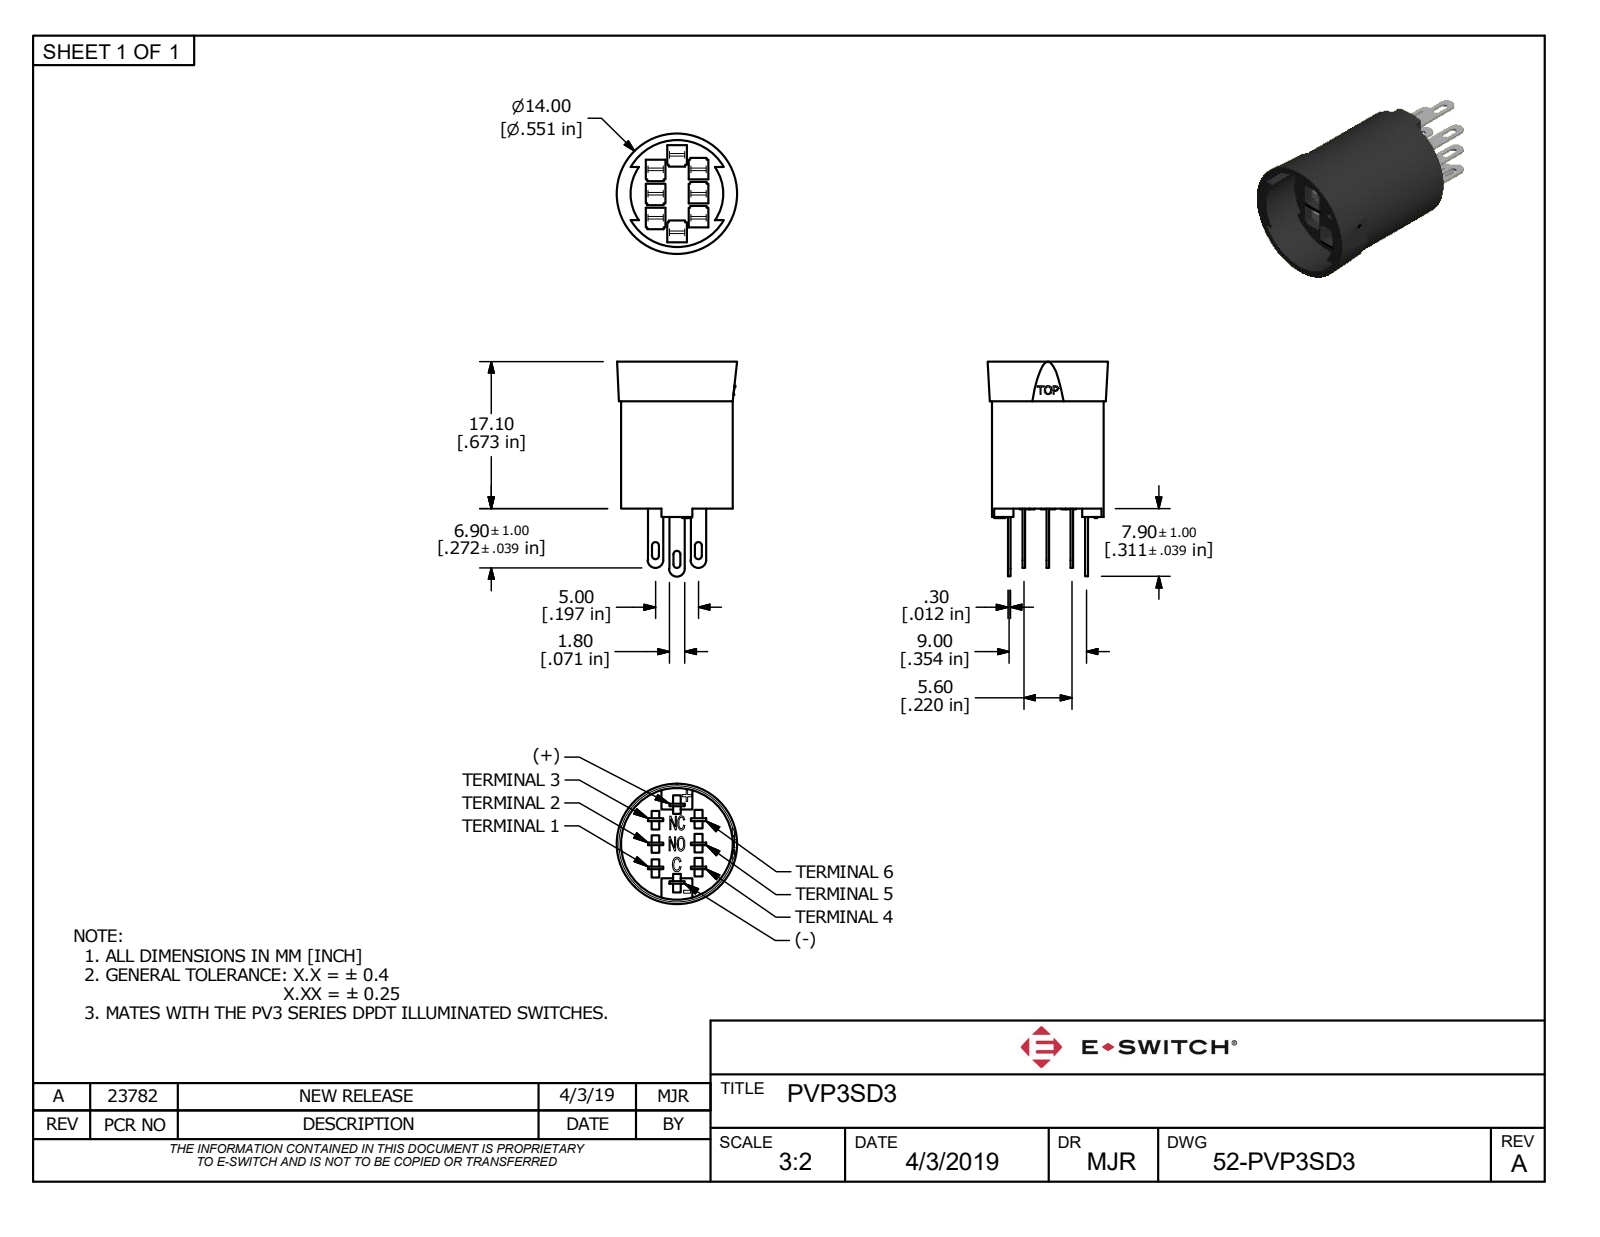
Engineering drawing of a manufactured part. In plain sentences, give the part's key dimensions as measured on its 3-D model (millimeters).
The part is named "PVP3SD3". Its 3-D file was written by "Autodesk Inventor 2018 (AP242_MANAGED_MODEL_BASED_3D_ENGINEERING_MIM_LF)". It is 1 solid with 407 faces: 312 planar, 45 cylindrical and 50 other. Overall it measures 25 by 14 by 14 millimeters. Its volume is 1 754 cubic millimeters and its surface area 1 917 square millimeters. Round bosses or shafts: 1 of diameter 13. Partial cylindrical surfaces (rounded edges, fillets, slot ends): 10 of radius 0.25, 6 of radius 0.4, 3 of radius 0.9, 2 of radius 6.25, 1 of radius 5.4. The main face-to-face distances are 2.8, 2.5, 7.3, 0.45, 1.7, 5.6, 4.5, 3.1, 1.8, 2.05.
